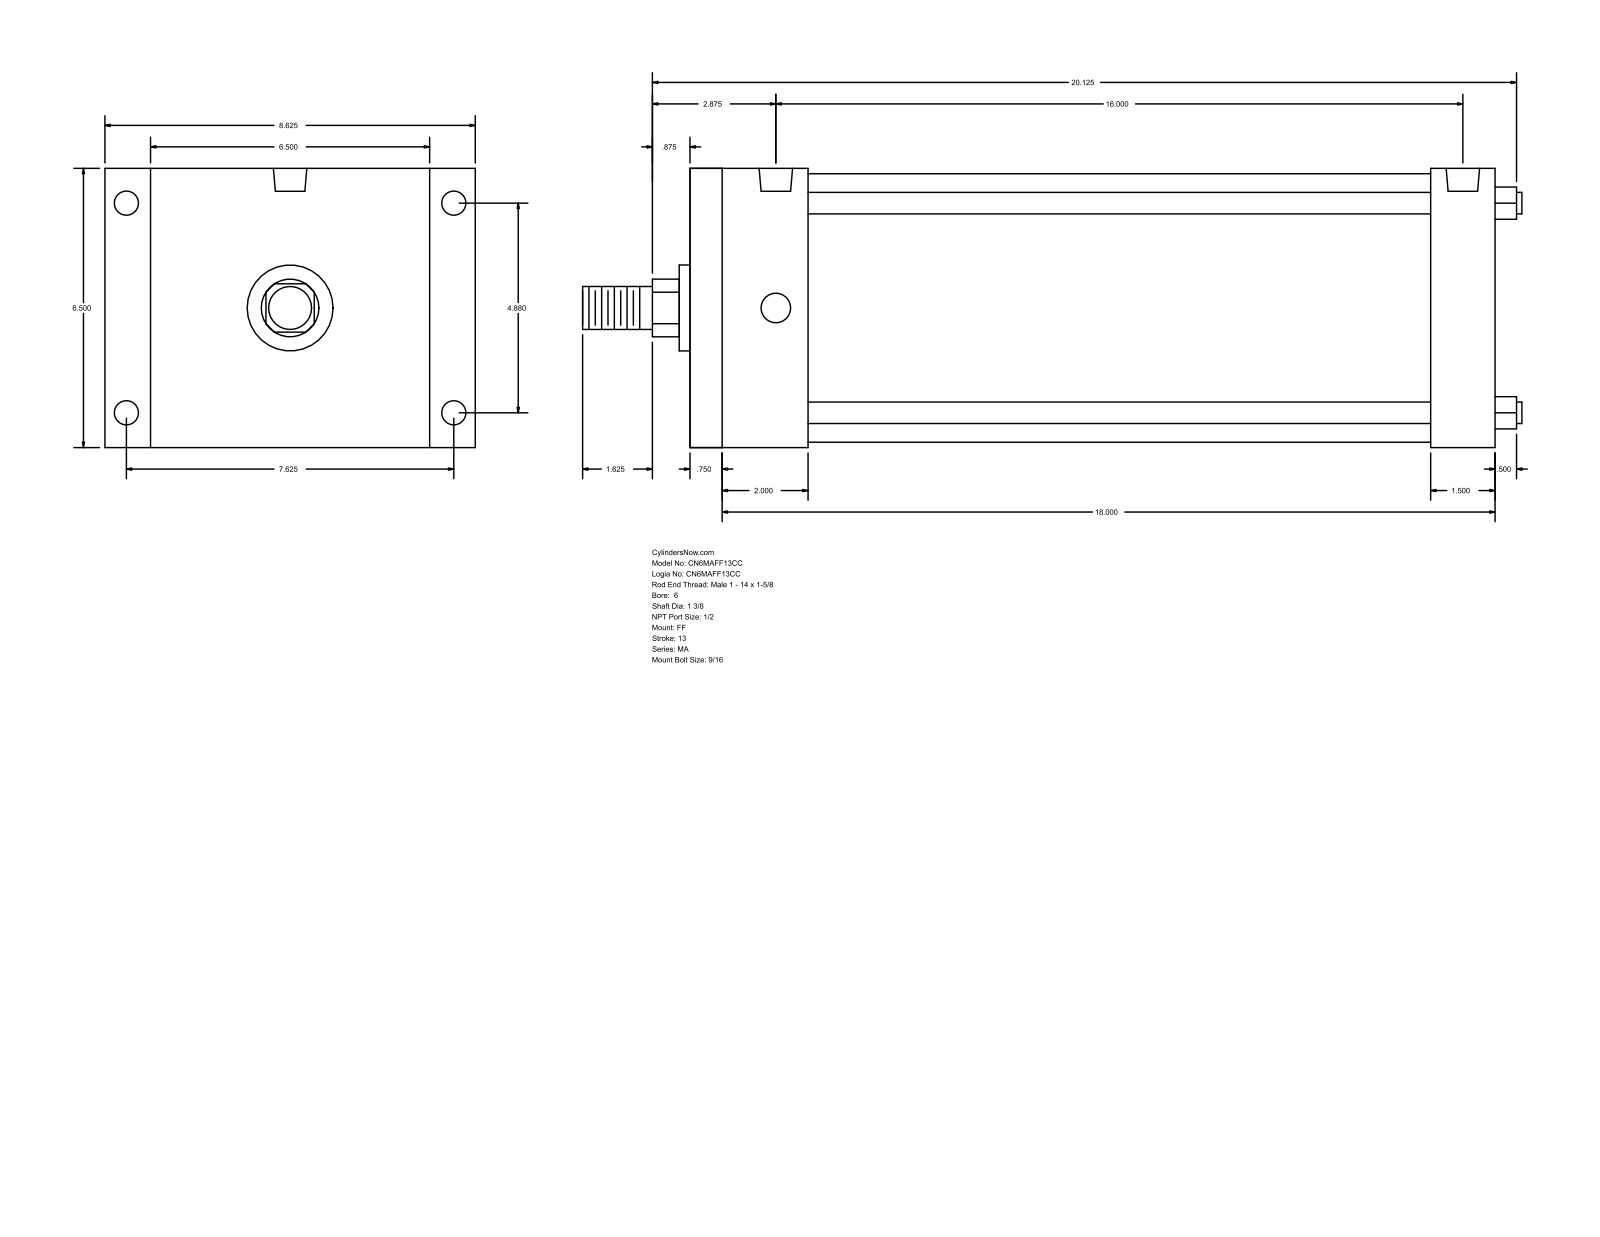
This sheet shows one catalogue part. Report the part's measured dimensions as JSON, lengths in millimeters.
{"part_name": "MA_FF__0600_1.375", "step_written_by": "GSSL Pune (CONFIG_CONTROL_DESIGN)", "units": "millimeters", "bodies": {"solids": 0, "faces": 92, "planar": 64, "cylindrical": 28, "other": 0}, "overall_size": [555.62, 219.07, 165.1], "round_holes": [[14.29, 4], [17.46, 4], [19.77, 2]], "round_bosses_or_shafts": [[12.7, 4], [158.75, 1], [50.8, 1], [34.92, 1], [25.4, 1]], "partial_cylinders_radius": [[17.06, 1]], "face_to_face_distances": [165.1, 476.25, 15.87, 460.38, 50.8, 422.28, 38.1, 66.67, 409.58, 438.15], "hole_center_spacings": [123.96, 193.68, 229.95, 409.58, 3.18, 406.4]}
